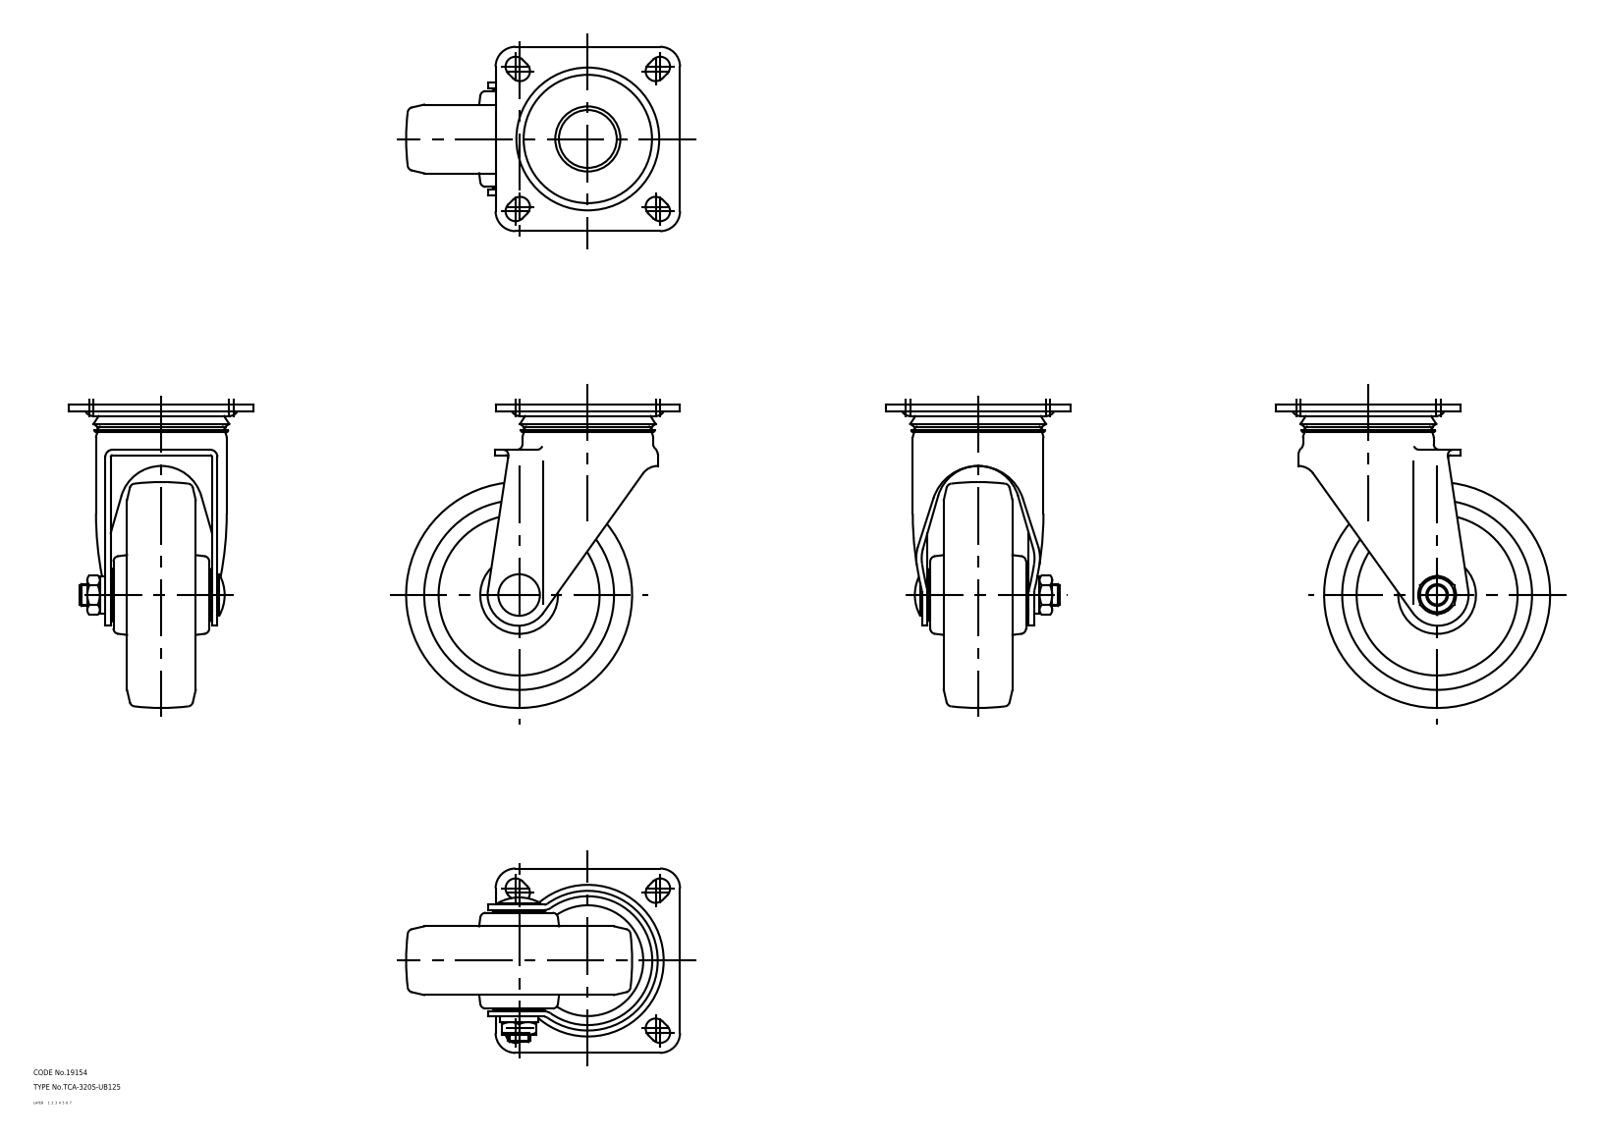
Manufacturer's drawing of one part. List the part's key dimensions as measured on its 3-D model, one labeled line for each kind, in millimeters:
Part name (STEP PRODUCT): wheel; mounting plate; main shaft; axle (+1 more)
STEP written by: CADfix (AUTOMOTIVE_DESIGN)
Units: millimetres
Bodies: 5 solids, 243 faces (0 planar, 0 cylindrical, 243 other)
Overall size (bounding box): 168 × 151.5 × 102
Volume: 586 600 mm³ · Surface area: 116 840 mm²
